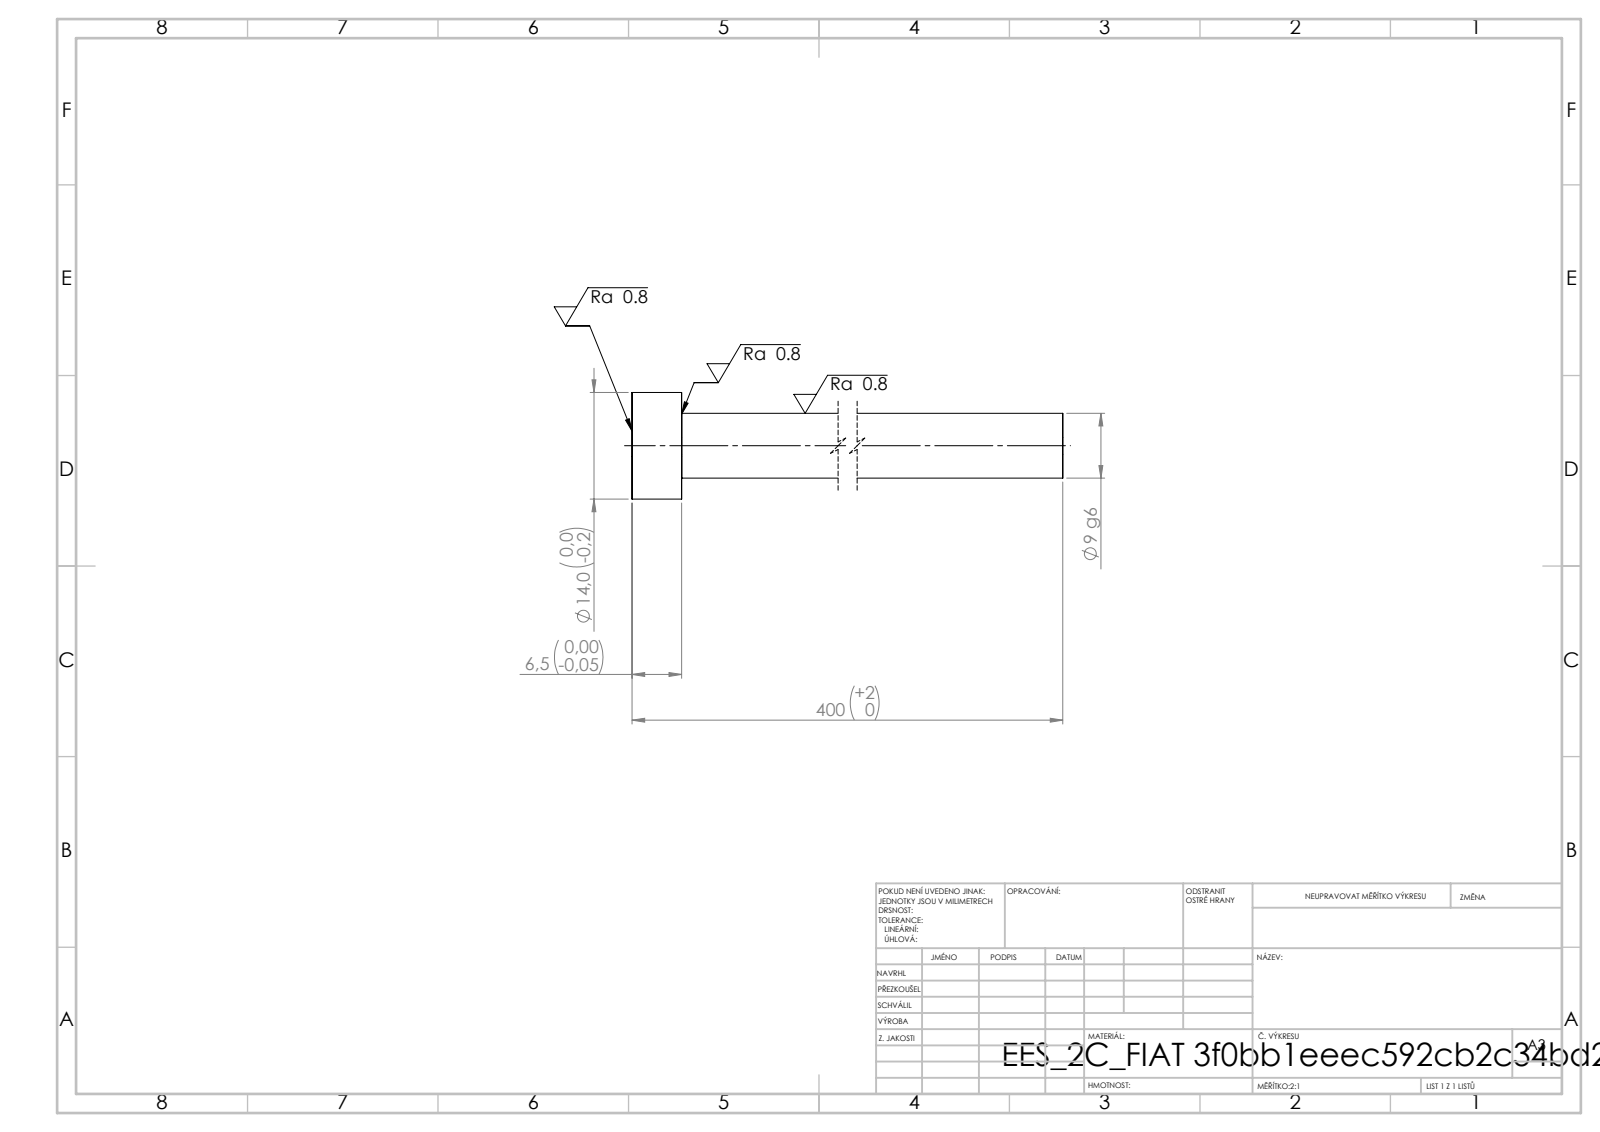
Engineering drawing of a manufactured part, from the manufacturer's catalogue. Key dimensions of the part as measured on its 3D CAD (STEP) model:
STEP written by: SolidWorks 2019 (CONFIG_CONTROL_DESIGN)
Units: millimetres
Bodies: 1 solid, 7 faces (3 planar, 4 cylindrical, 0 other)
Overall size (bounding box): 400 × 14 × 14
Volume: 23 330 mm³ · Surface area: 11 102 mm²
Round bosses / shafts (diameter × count): ⌀14 ×1, ⌀8.5 ×1
Main face-to-face distances: 6.5, 400, 393.5
